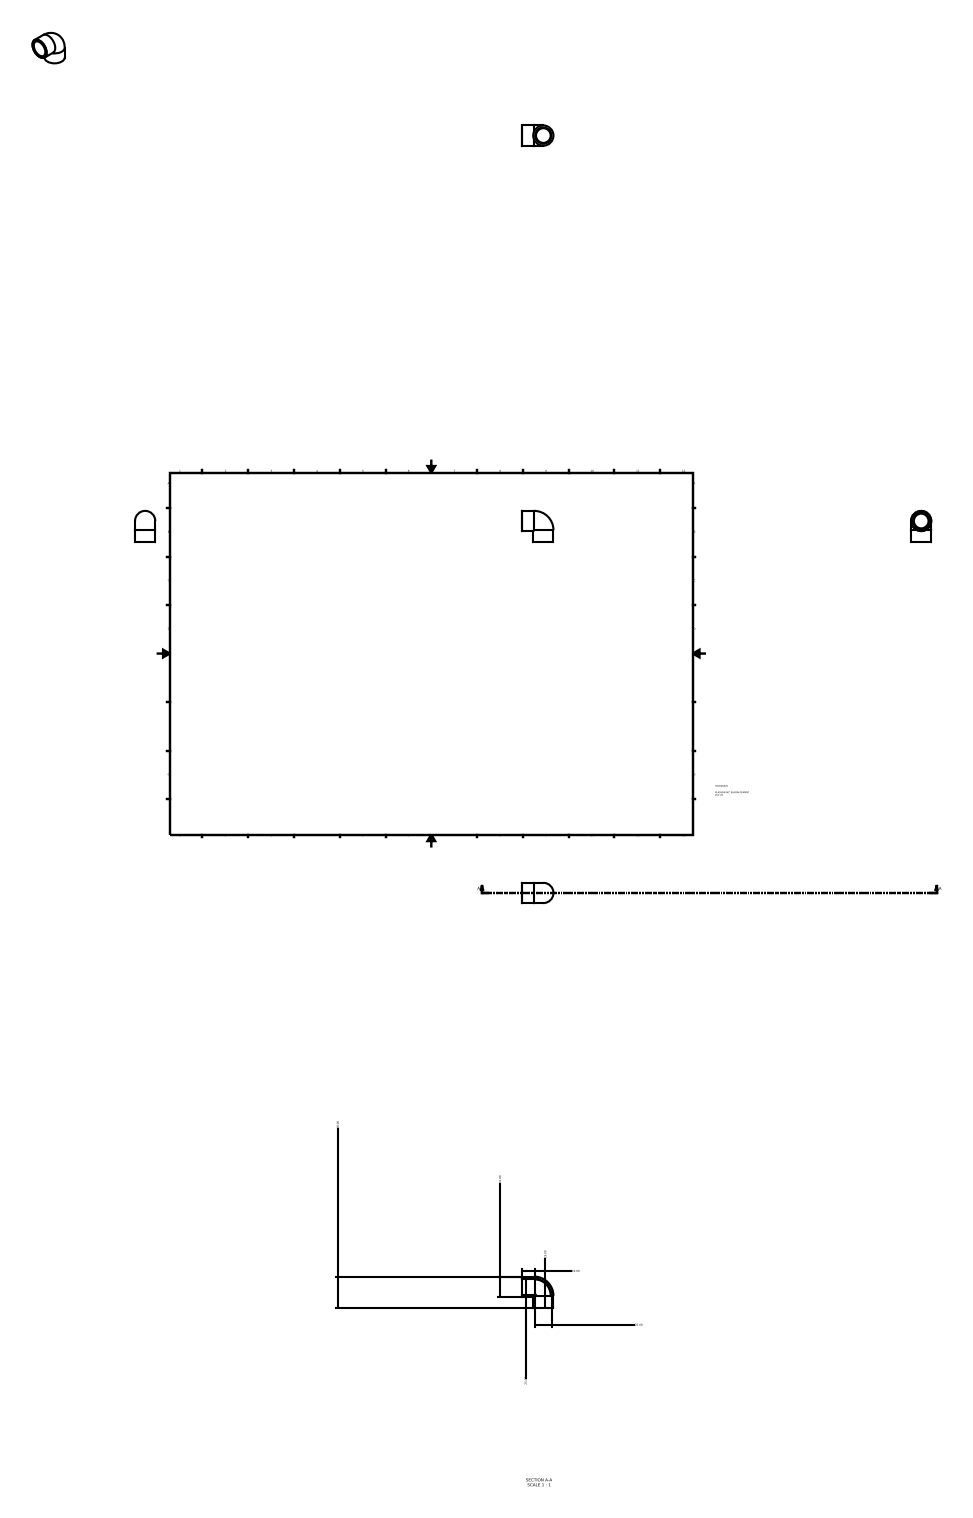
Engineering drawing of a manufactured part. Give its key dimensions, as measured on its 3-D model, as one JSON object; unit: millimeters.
{"part_name": "050500025", "step_written_by": "Autodesk Inventor 2015 (AUTOMOTIVE_DESIGN)", "units": "millimeters", "bodies": {"solids": 1, "faces": 11, "planar": 4, "cylindrical": 4, "other": 3}, "overall_size": [48, 48, 31], "volume_mm3": 17625, "surface_area_mm2": 10931, "round_holes": [[25, 2]], "round_bosses_or_shafts": [[31, 2]], "face_to_face_distances": [19]}
